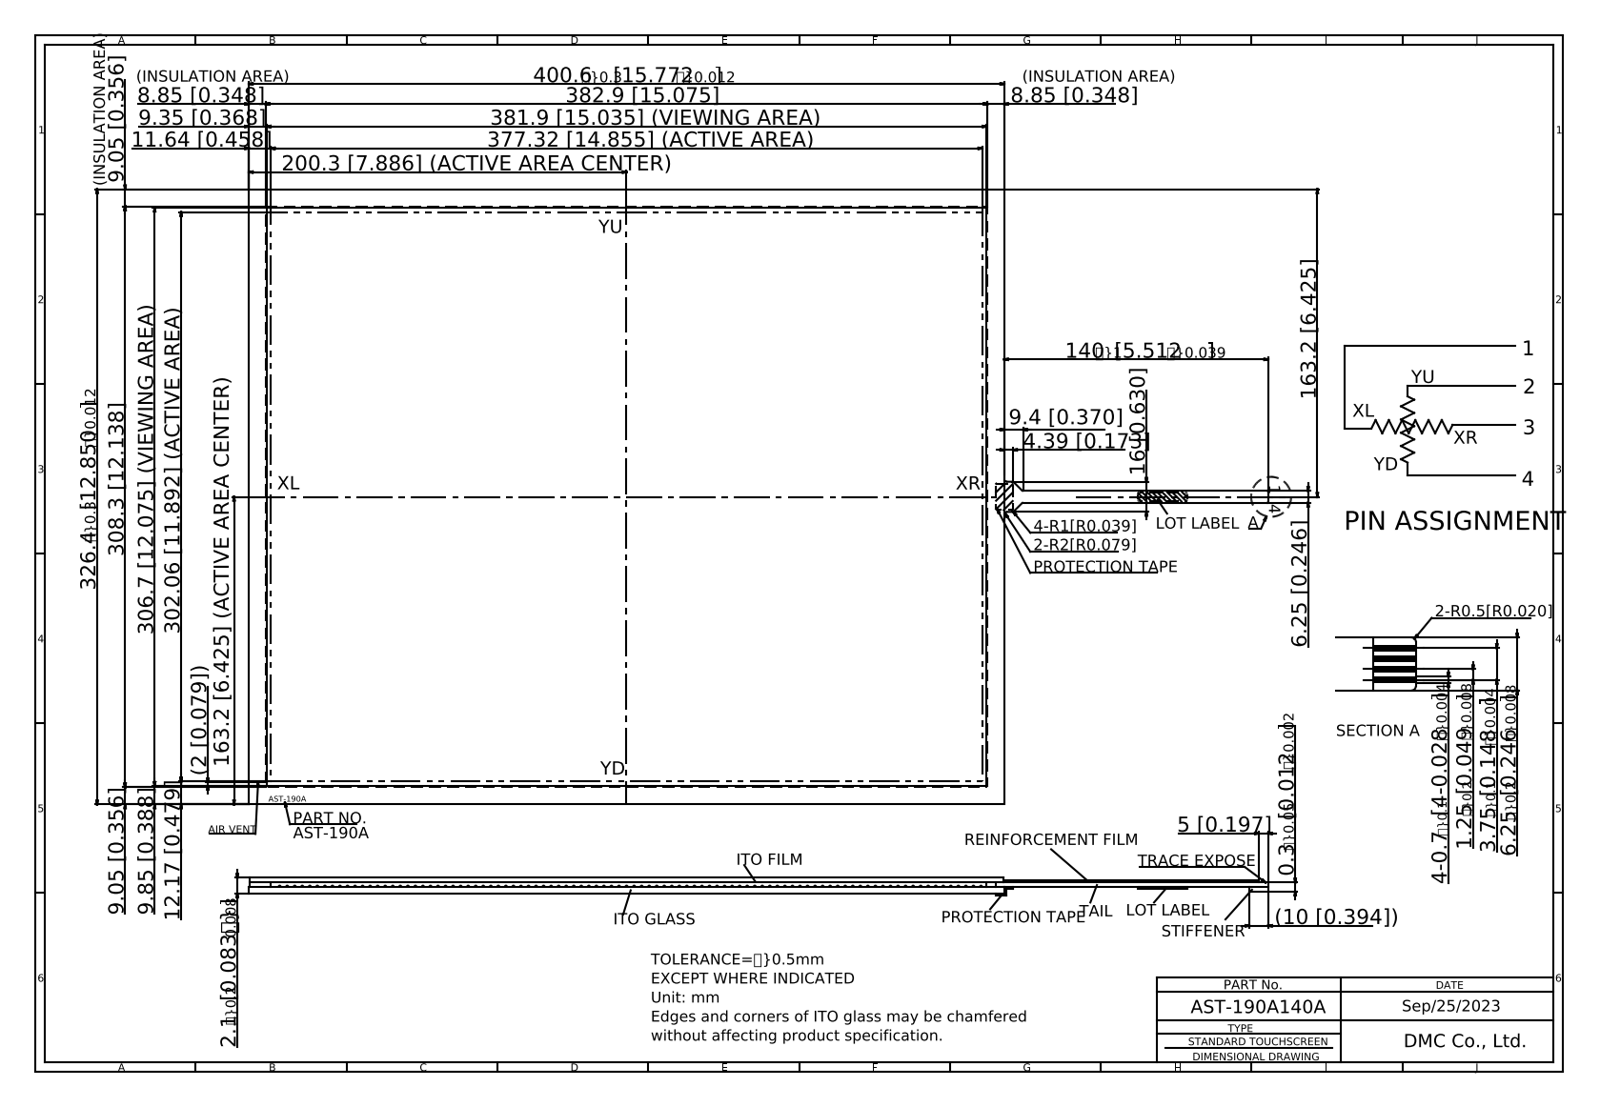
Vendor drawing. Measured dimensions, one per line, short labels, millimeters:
name: AST-190A140A
written by: Autodesk Inventor 2020 (CONFIG_CONTROL_DESIGN)
unit: mm
bodies: 1 solid, 48 faces (45 planar, 3 cylindrical, 0 other)
size: 620.72 × 456.96 × 2.1
volume: 274 382 mm³; area: 266 763 mm²
rounds: 2× R0.5, 1× R1
face distances: 2.1, 2, 1.9, 1.8, 326.4, 400.6, 9.85, 316.55, 12.17, 314.23
